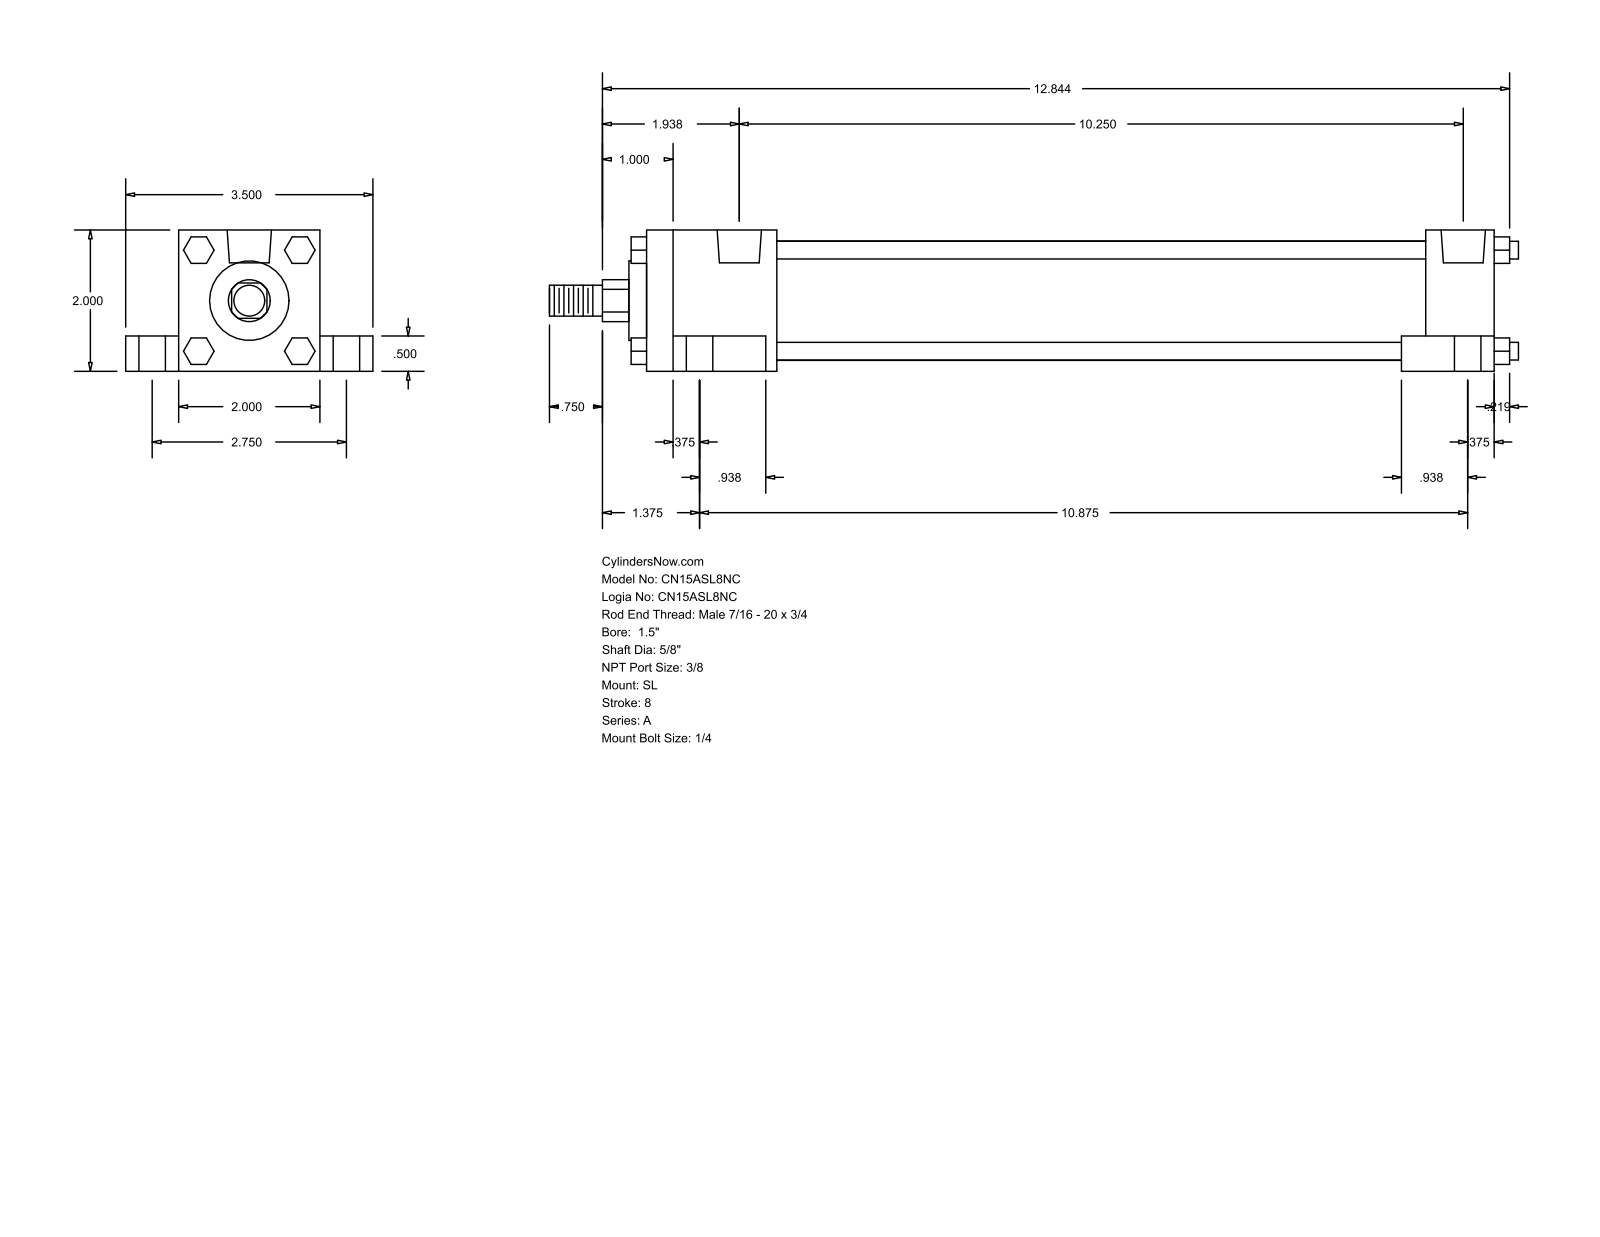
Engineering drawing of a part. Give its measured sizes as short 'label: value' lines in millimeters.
name: A_SL__0150_0.625
written by: GSSL Pune (CONFIG_CONTROL_DESIGN)
unit: mm
bodies: 0 solids, 148 faces (112 planar, 36 cylindrical, 0 other)
size: 348.46 × 88.9 × 50.8
holes: 4× ⌀5.56, 4× ⌀9.53, 4× ⌀15.88, 2× ⌀15.93
bosses: 4× ⌀6.35, 1× ⌀42.93, 1× ⌀28.57, 1× ⌀15.88, 1× ⌀11.11
rounds: 1× R7.54
face distances: 50.8, 19.05, 38.1, 12.7, 69.85, 304.8, 9.52, 33.34, 280.19, 24.61
hole spacings: 3.97, 34.96, 35.36, 37.73, 39.41, 69.84, 252.41, 256.38
